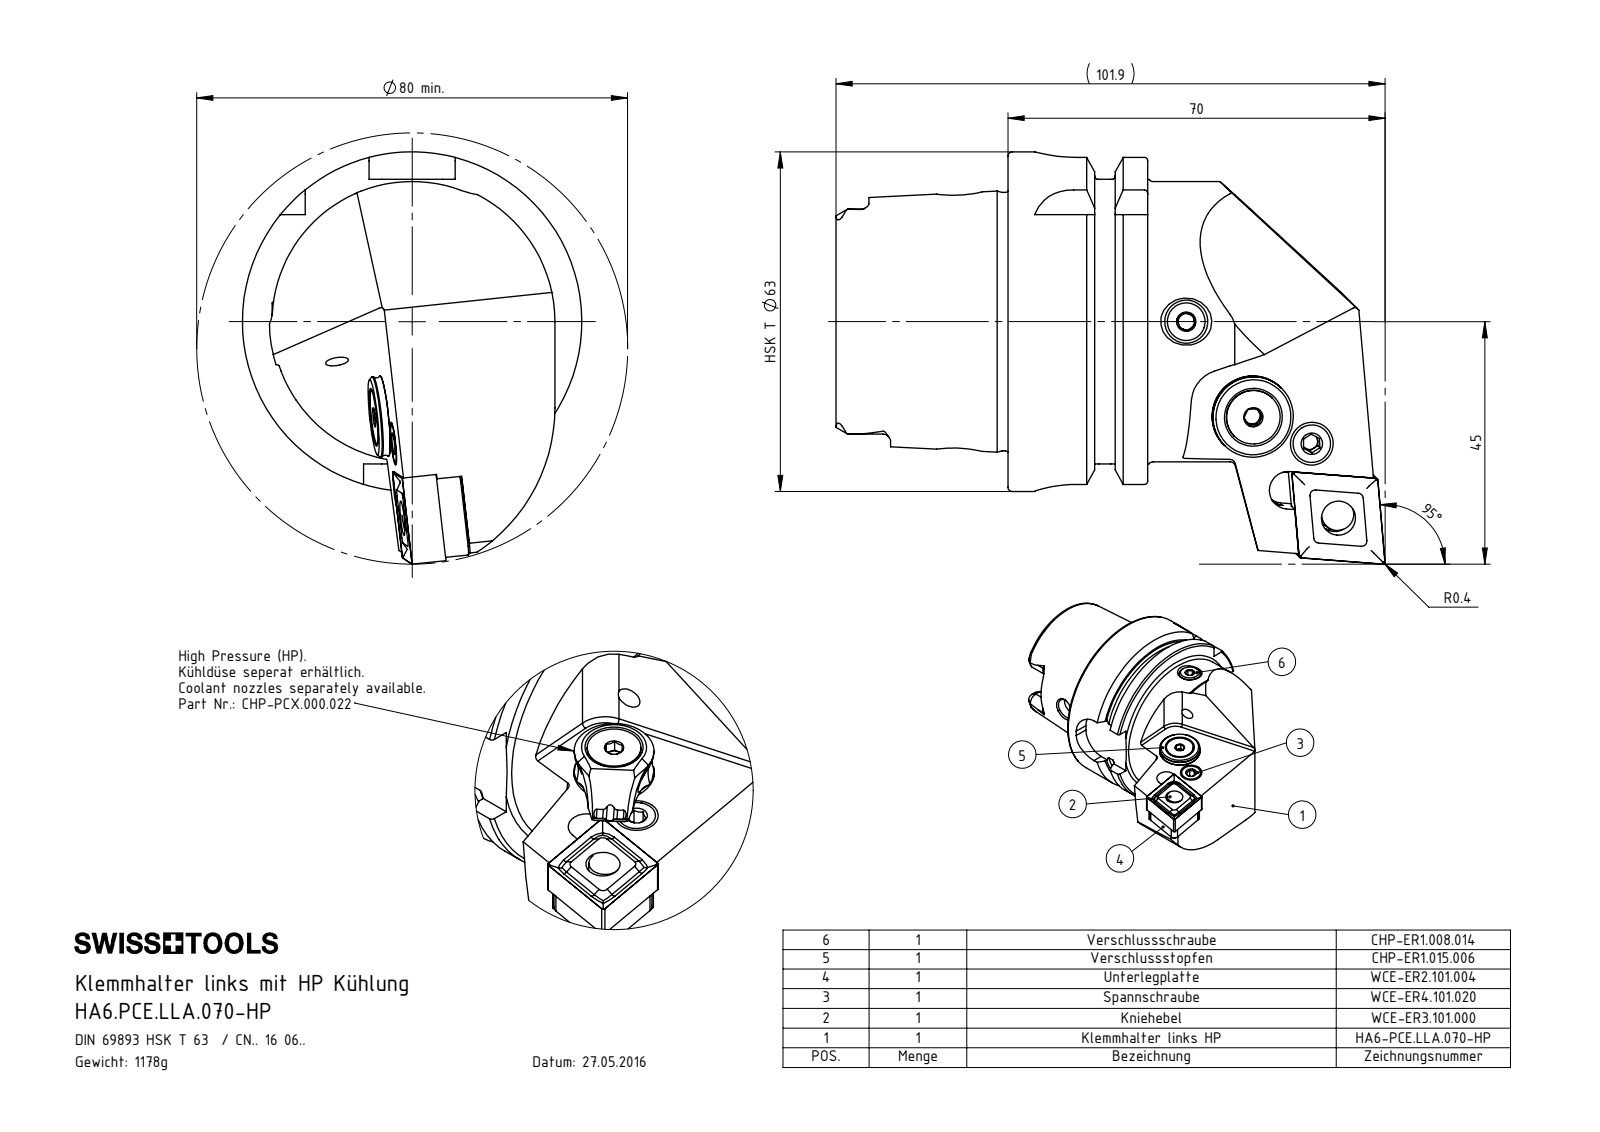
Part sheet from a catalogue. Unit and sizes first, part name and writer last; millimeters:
Units: millimetres
Overall size (bounding box): 101.9 × 76.5 × 63
Round holes (diameter × count): ⌀4.2 ×2, ⌀5 ×2, ⌀7 ×2, ⌀8.4 ×2, ⌀1.2 ×1, ⌀2 ×1, ⌀2.5 ×1, ⌀3 ×1, ⌀5.2 ×1, ⌀6.35 ×1, ⌀7.5 ×1, ⌀8.05 ×1
Round bosses / shafts (diameter × count): ⌀8 ×2, ⌀63 ×1, ⌀54.95 ×1, ⌀52 ×1, ⌀47.94 ×1, ⌀15 ×1, ⌀13.4 ×1, ⌀10 ×1
Partial cylindrical surfaces — rounded edges, fillets, slot ends (radius × count): R1.4 ×6, R3.5 ×5, R0.4 ×4, R1.5 ×4, R2.88 ×4, R8 ×4, R0.3 ×2, R0.8 ×2
Main face-to-face distances: 25.95, 16, 9.95, 6.05, 31.9, 41.85, 57.85, 52.8, 21.8, 11.85
Hole centre spacings: 4.5, 10.93, 21.85, 25.01, 4.51, 12.29, 12.3, 14.76
Volume: 149 257 mm³ · Surface area: 36 849 mm²
Bodies: 11 solids, 508 faces (163 planar, 139 cylindrical, 206 other)
Part name (STEP PRODUCT): WCE-ER4.101.020_A; HA6.PCE.LLA.070-HP; WCE-ER3.101.000_A; HA6-PCE.LLA.070-HP_B (+8 more)
STEP written by: SolidWorks 2017 (AUTOMOTIVE_DESIGN)
